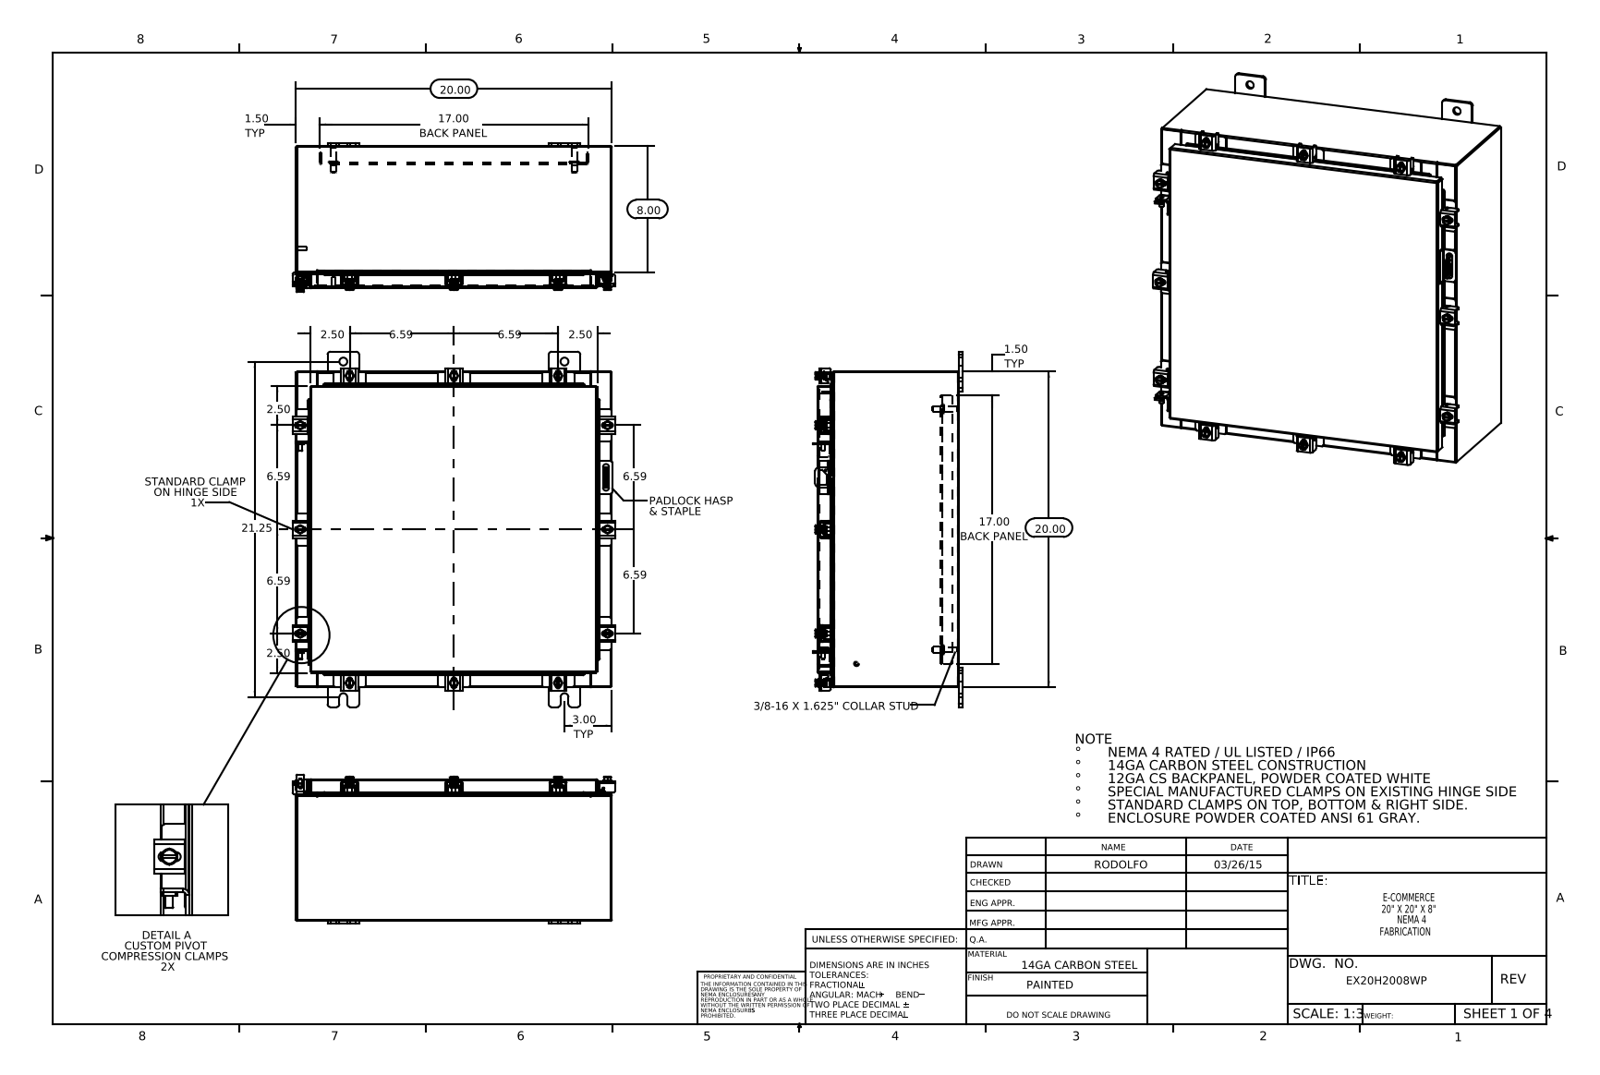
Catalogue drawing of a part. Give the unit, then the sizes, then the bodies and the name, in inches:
Units: inches
Overall size (bounding box): 22.5 × 20.421 × 9.453
Round holes (diameter × count): ⌀0.213 ×12, ⌀0.26 ×12, ⌀0.5 ×8, ⌀0.125 ×1, ⌀0.25 ×1
Round bosses / shafts (diameter × count): ⌀0.5 ×12, ⌀0.25 ×12, ⌀0.399 ×10, ⌀0.625 ×4, ⌀0.375 ×4, ⌀0.33 ×4, ⌀0.315 ×2, ⌀0.236 ×2
Partial cylindrical surfaces — rounded edges, fillets, slot ends (radius × count): R0.06 ×54, R0.013 ×24, R0.141 ×24, R0.19 ×24, R0.088 ×22, R0.12 ×22, R0.09 ×18, R0.05 ×17
Main face-to-face distances: 0.075, 8.9, 19.925, 8.975, 8.826, 19.85, 20, 0.104, 1, 1.075
Hole centre spacings: 6.594, 10.217, 16.617, 18.998, 20.539, 2.34, 14.374, 17.381
Volume: 161.6 in³ · Surface area: 4 054 in²
Bodies: 81 solids, 2018 faces (1075 planar, 783 cylindrical, 160 other)
Part name (STEP PRODUCT): N-WMT04X30402202210-00 Clamp Top; N-WMT04X30402202210-00 22101002; ATEX CLAMP HINGE BRAKET; 30X10 Clamp Bracket2 (+8 more)
STEP written by: SolidWorks 2014 (CONFIG_CONTROL_DESIGN)
